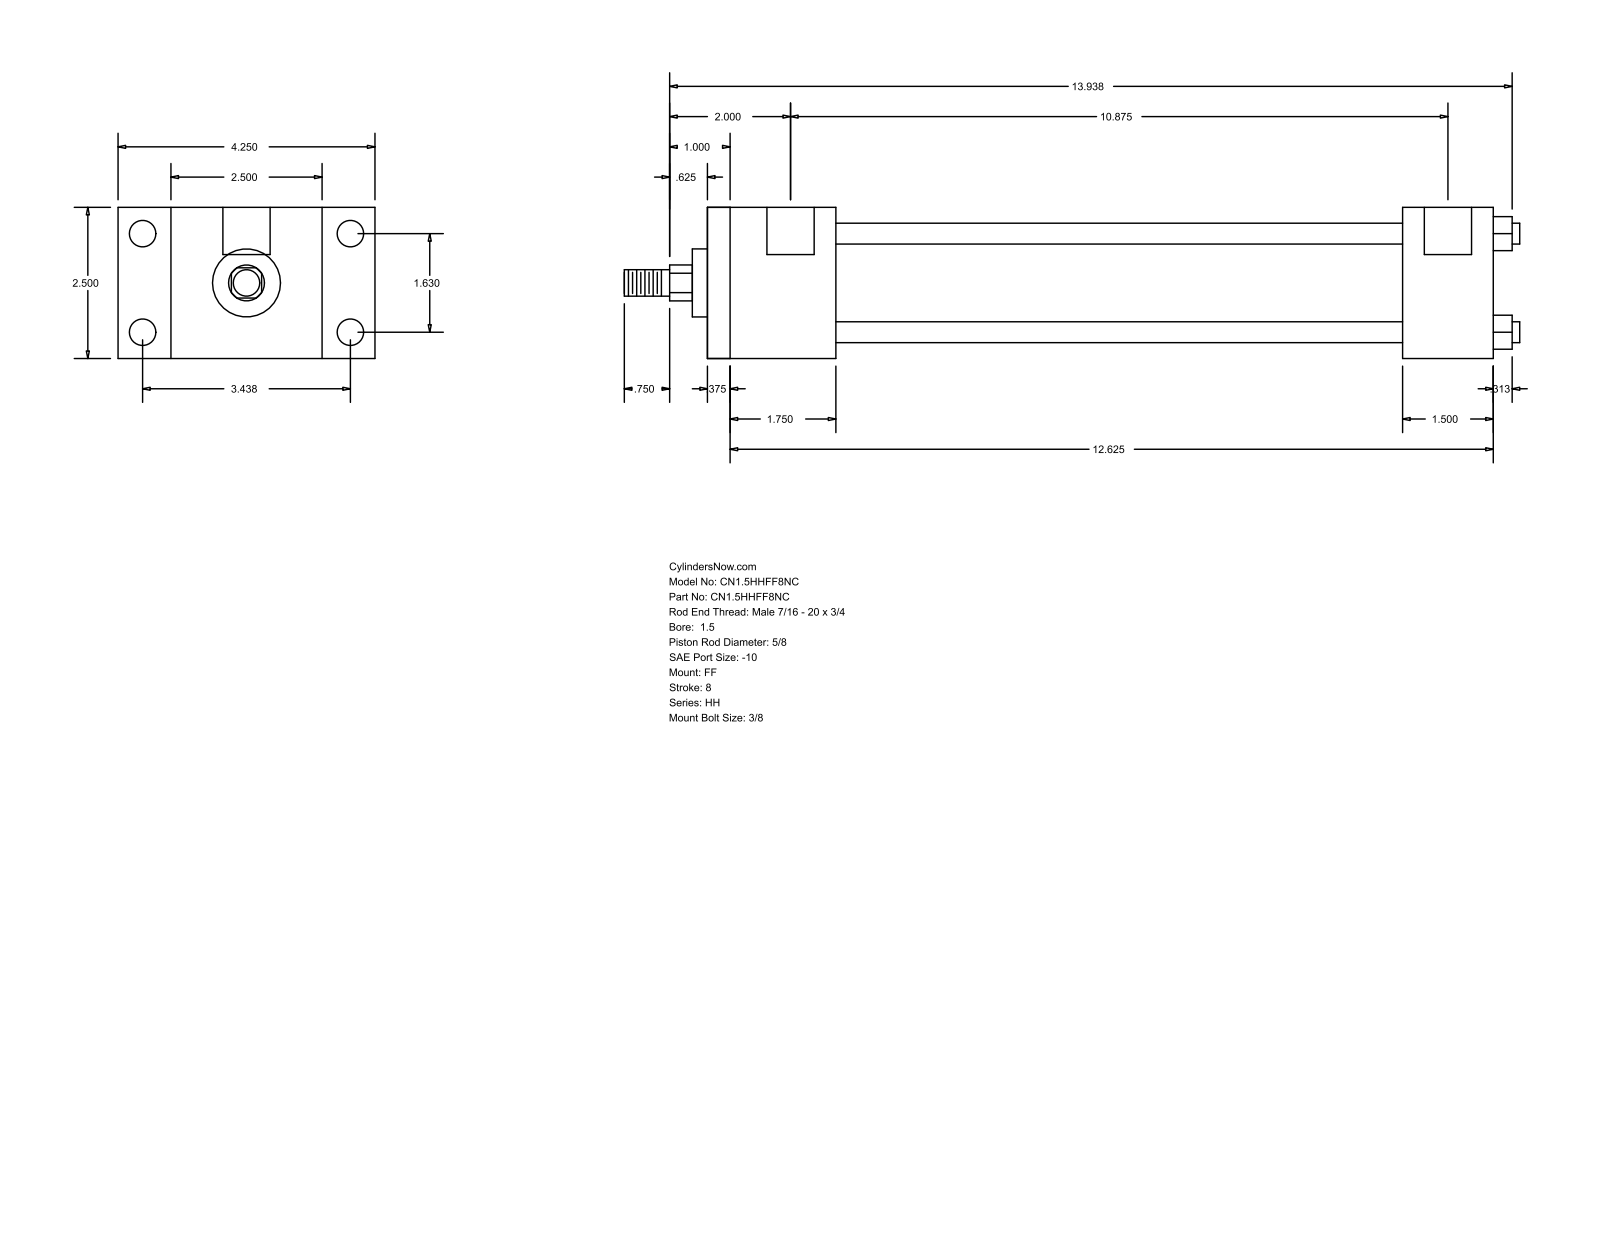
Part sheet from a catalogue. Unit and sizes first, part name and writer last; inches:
Units: inches
Overall size (bounding box): 14.813 × 4.25 × 2.5
Round holes (diameter × count): ⌀0.219 ×4, ⌀0.438 ×4, ⌀0.781 ×2
Round bosses / shafts (diameter × count): ⌀0.345 ×4, ⌀1.75 ×1, ⌀1.125 ×1, ⌀0.625 ×1, ⌀0.437 ×1
Partial cylindrical surfaces — rounded edges, fillets, slot ends (radius × count): R0.297 ×1
Main face-to-face distances: 2.5, 13, 0.375, 12.625, 1.75, 2.125, 10.875, 11.5, 11.125, 9.375
Hole centre spacings: 0.063, 1.63, 3.438, 3.805, 10.937, 11, 10.875
Bodies: 0 solids, 92 faces (64 planar, 28 cylindrical, 0 other)
Part name (STEP PRODUCT): HH_FF__0150_0.625
STEP written by: GSSL Pune (CONFIG_CONTROL_DESIGN)
